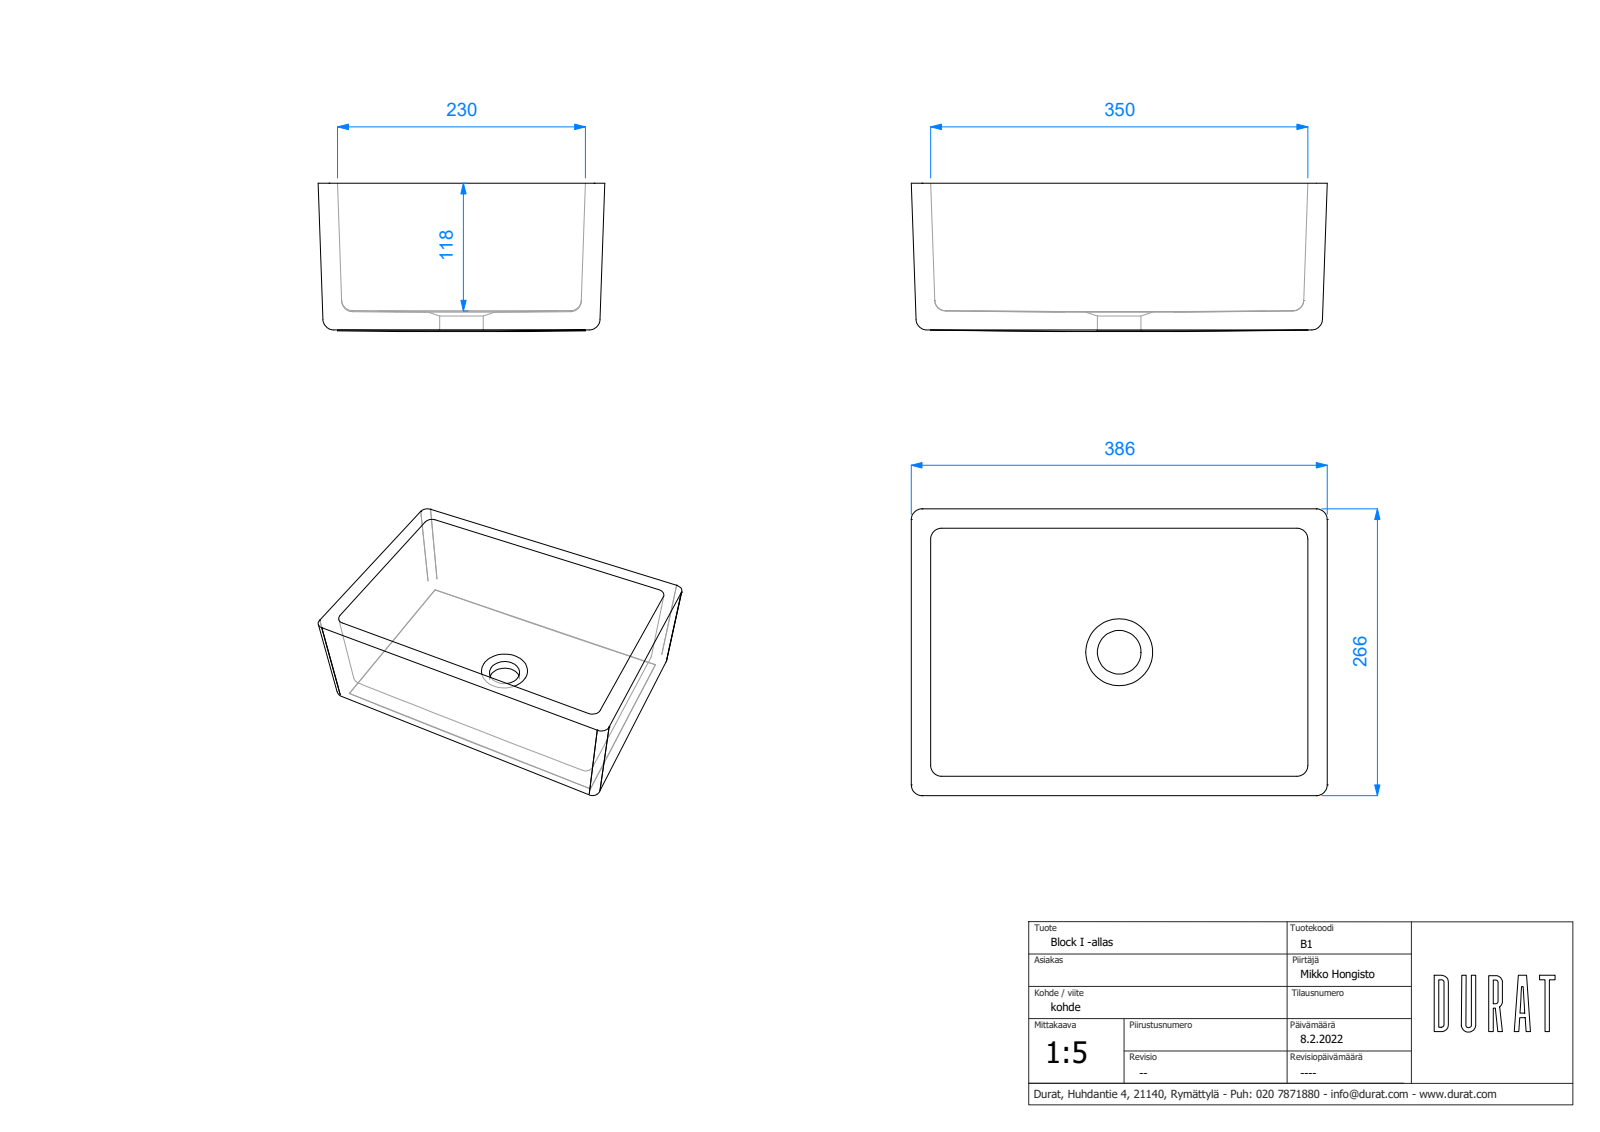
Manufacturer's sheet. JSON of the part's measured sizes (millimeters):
{"step_written_by": "ST-DEVELOPER v15 (AUTOMOTIVE_DESIGN)", "units": "millimeters", "bodies": {"solids": 0, "faces": 50, "planar": 16, "cylindrical": 0, "other": 34}, "overall_size": [386.02, 266.02, 137.59], "face_to_face_distances": [18.01, 17.98, 137.59, 18, 119.59, 1.59, 16.41, 136, 230, 350]}
